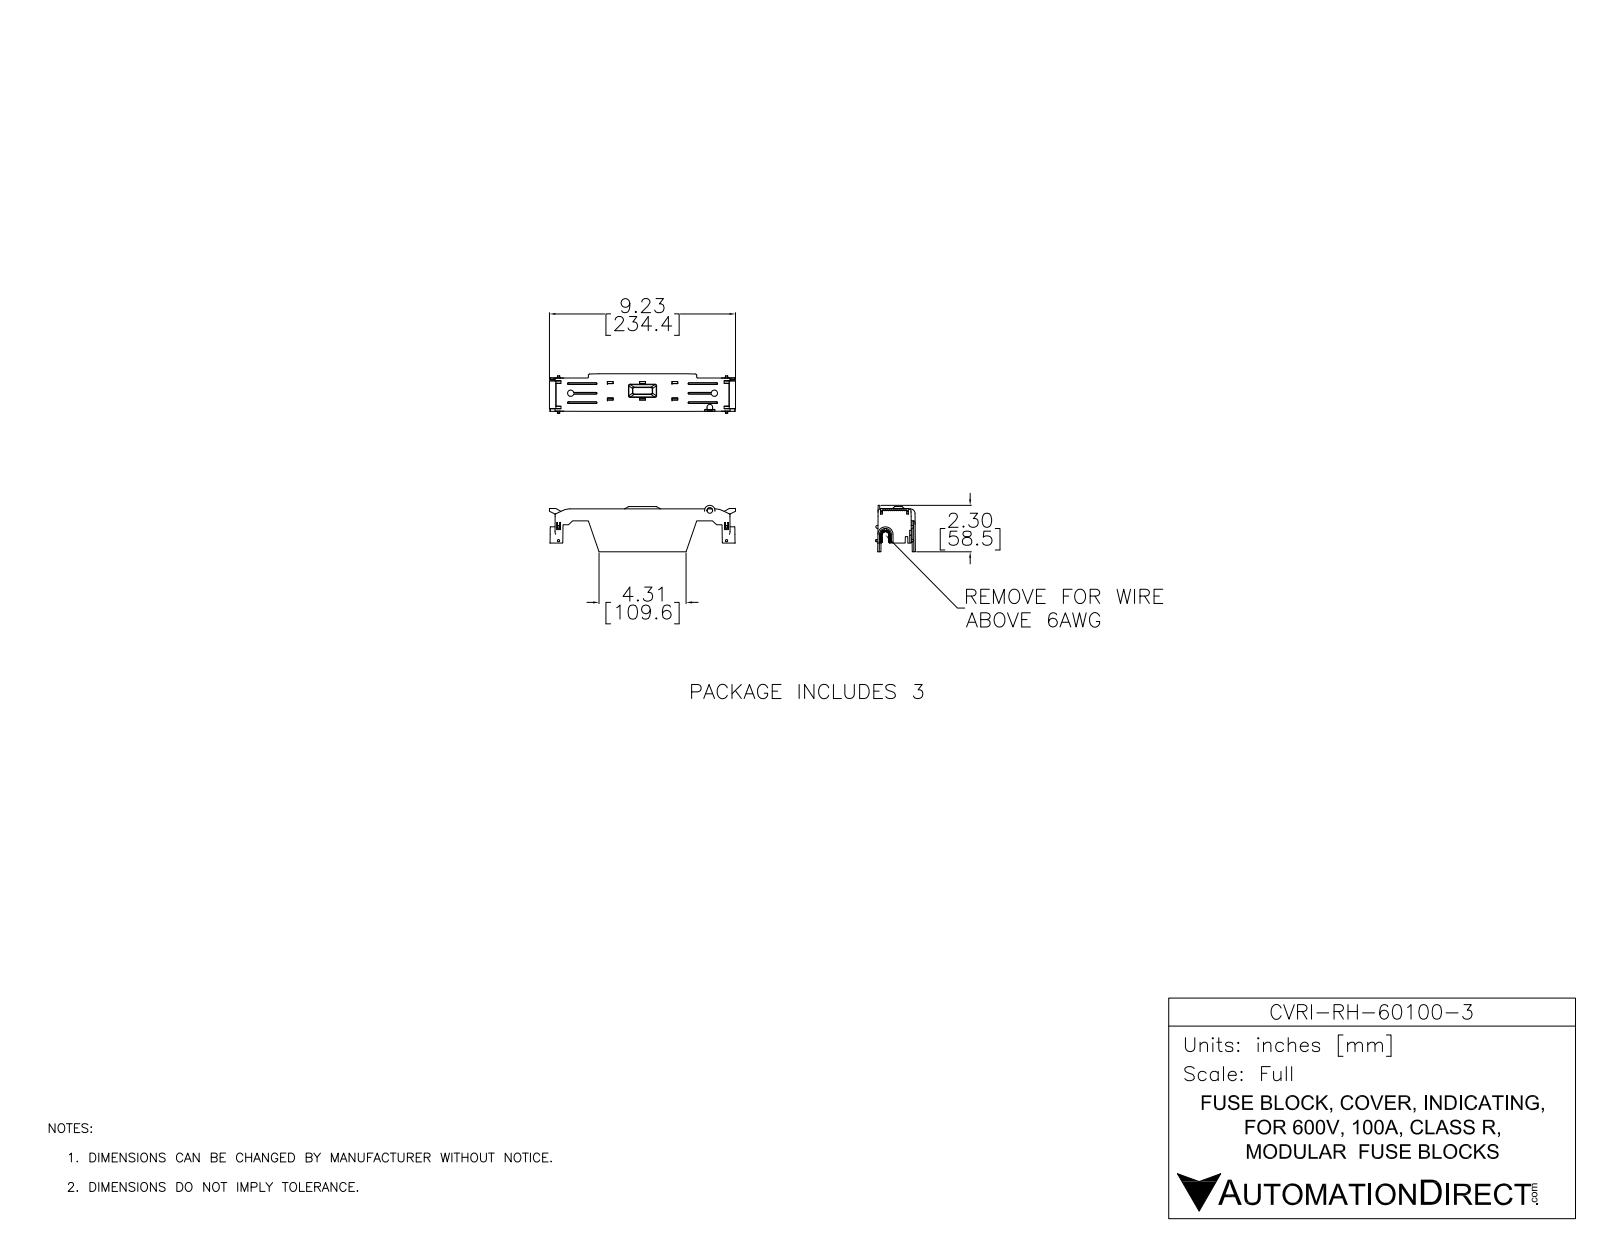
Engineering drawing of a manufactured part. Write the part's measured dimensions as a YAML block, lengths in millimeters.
part_name: "CVRI-RH-60100-3"
step_written_by: "SolidWorks 2017 (AUTOMOTIVE_DESIGN)"
units: millimeters
bodies: {solids: 1, faces: 1436, planar: 948, cylindrical: 102, other: 386}
overall_size: [234.4, 58.5, 49.9]
volume: 67020
surface_area: 71030
round_holes:
  - {diameter: 7, count: 1}
partial_cylinders:
  - {radius: 1, count: 18}
  - {radius: 3, count: 14}
  - {radius: 0.8, count: 6}
  - {radius: 1.5, count: 4}
  - {radius: 0.3, count: 2}
  - {radius: 0.5, count: 2}
  - {radius: 4.2, count: 2}
  - {radius: 16, count: 2}
face_to_face_distances: [2, 5, 3, 7, 4, 20.4, 25.1, 27.1, 30.1, 32.1]
